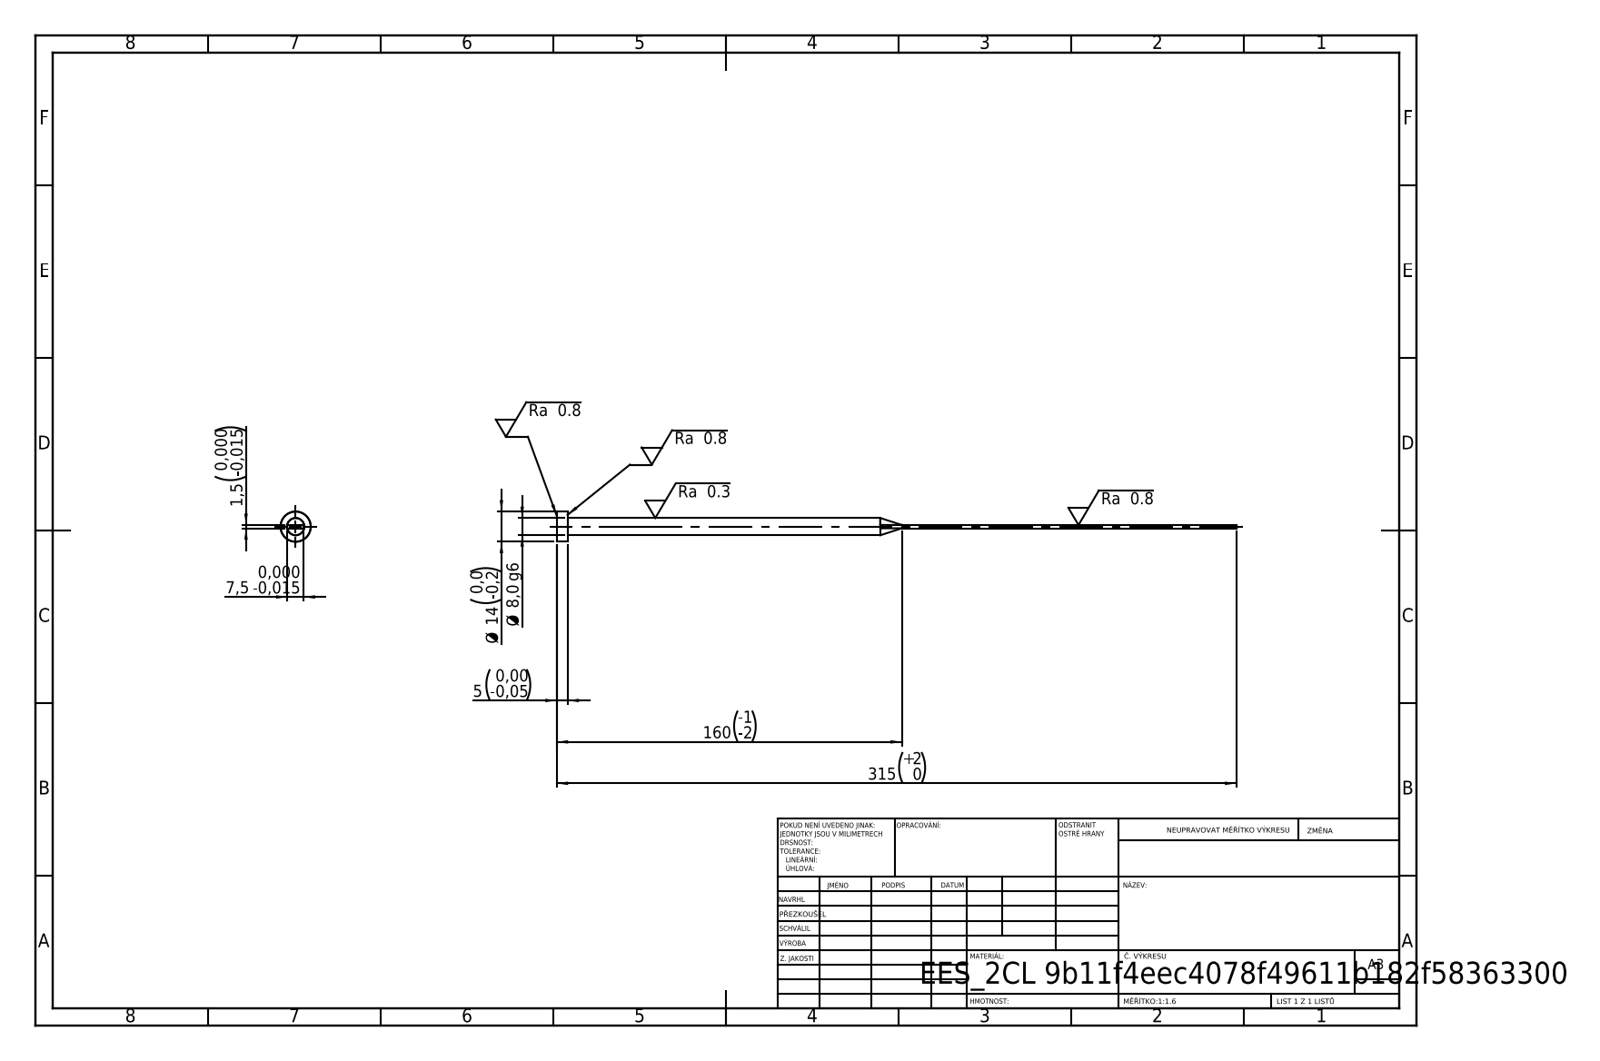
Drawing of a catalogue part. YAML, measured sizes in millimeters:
step_written_by: "SolidWorks 2019 (CONFIG_CONTROL_DESIGN)"
units: millimeters
bodies: {solids: 1, faces: 15, planar: 7, cylindrical: 4, other: 4}
overall_size: [315, 14, 14]
volume: 10094
surface_area: 7134
round_bosses_or_shafts:
  - {diameter: 14, count: 1}
  - {diameter: 8, count: 1}
face_to_face_distances: [1.5, 7.5, 5, 315, 310]
